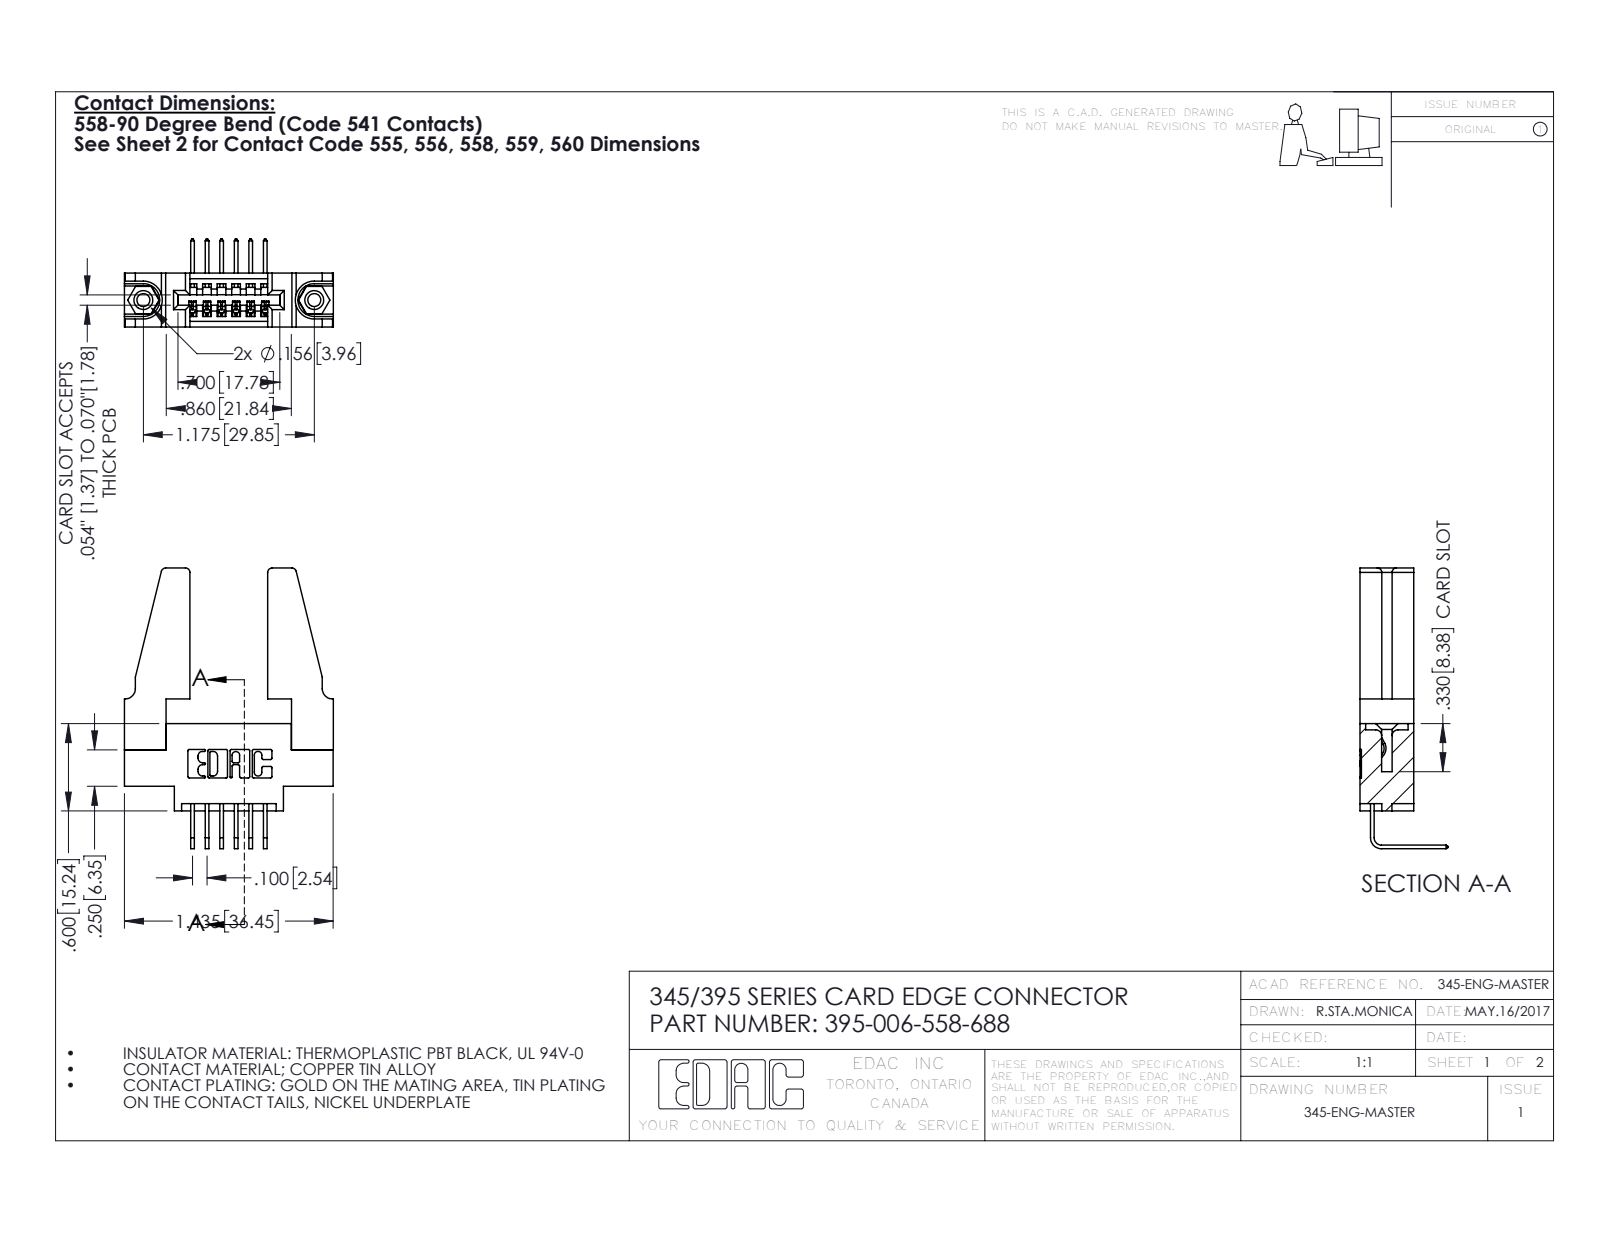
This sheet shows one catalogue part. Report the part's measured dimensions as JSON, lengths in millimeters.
{"part_name": "345-292-001_558 Tail - 2; 345-250-001_345-250-001-102; 345-220-078_345-220-088; 345 Part_0.170 Offset - 0.156 Dia-TH (+1 more)", "step_written_by": "SolidWorks 2016 (CONFIG_CONTROL_DESIGN)", "units": "millimeters", "bodies": {"solids": 11, "faces": 614, "planar": 408, "cylindrical": 190, "other": 16}, "overall_size": [49, 36.5, 15.4], "volume_mm3": 6330, "surface_area_mm2": 6974, "round_holes": [[2.3, 2], [3.2, 2], [4, 2], [1.6, 1]], "round_bosses_or_shafts": [[3.9, 2]], "partial_cylinders_radius": [[0.3, 22], [0.2, 12], [0.8, 8], [0.2, 6], [0.8, 6], [0.7, 3], [0.8, 2], [1, 2]], "face_to_face_distances": [9.4, 1.8, 7.6, 5.1, 3.8, 3.8, 2.5, 6.9, 0.6, 5.6], "hole_center_spacings": [6.9, 24, 29.8]}
